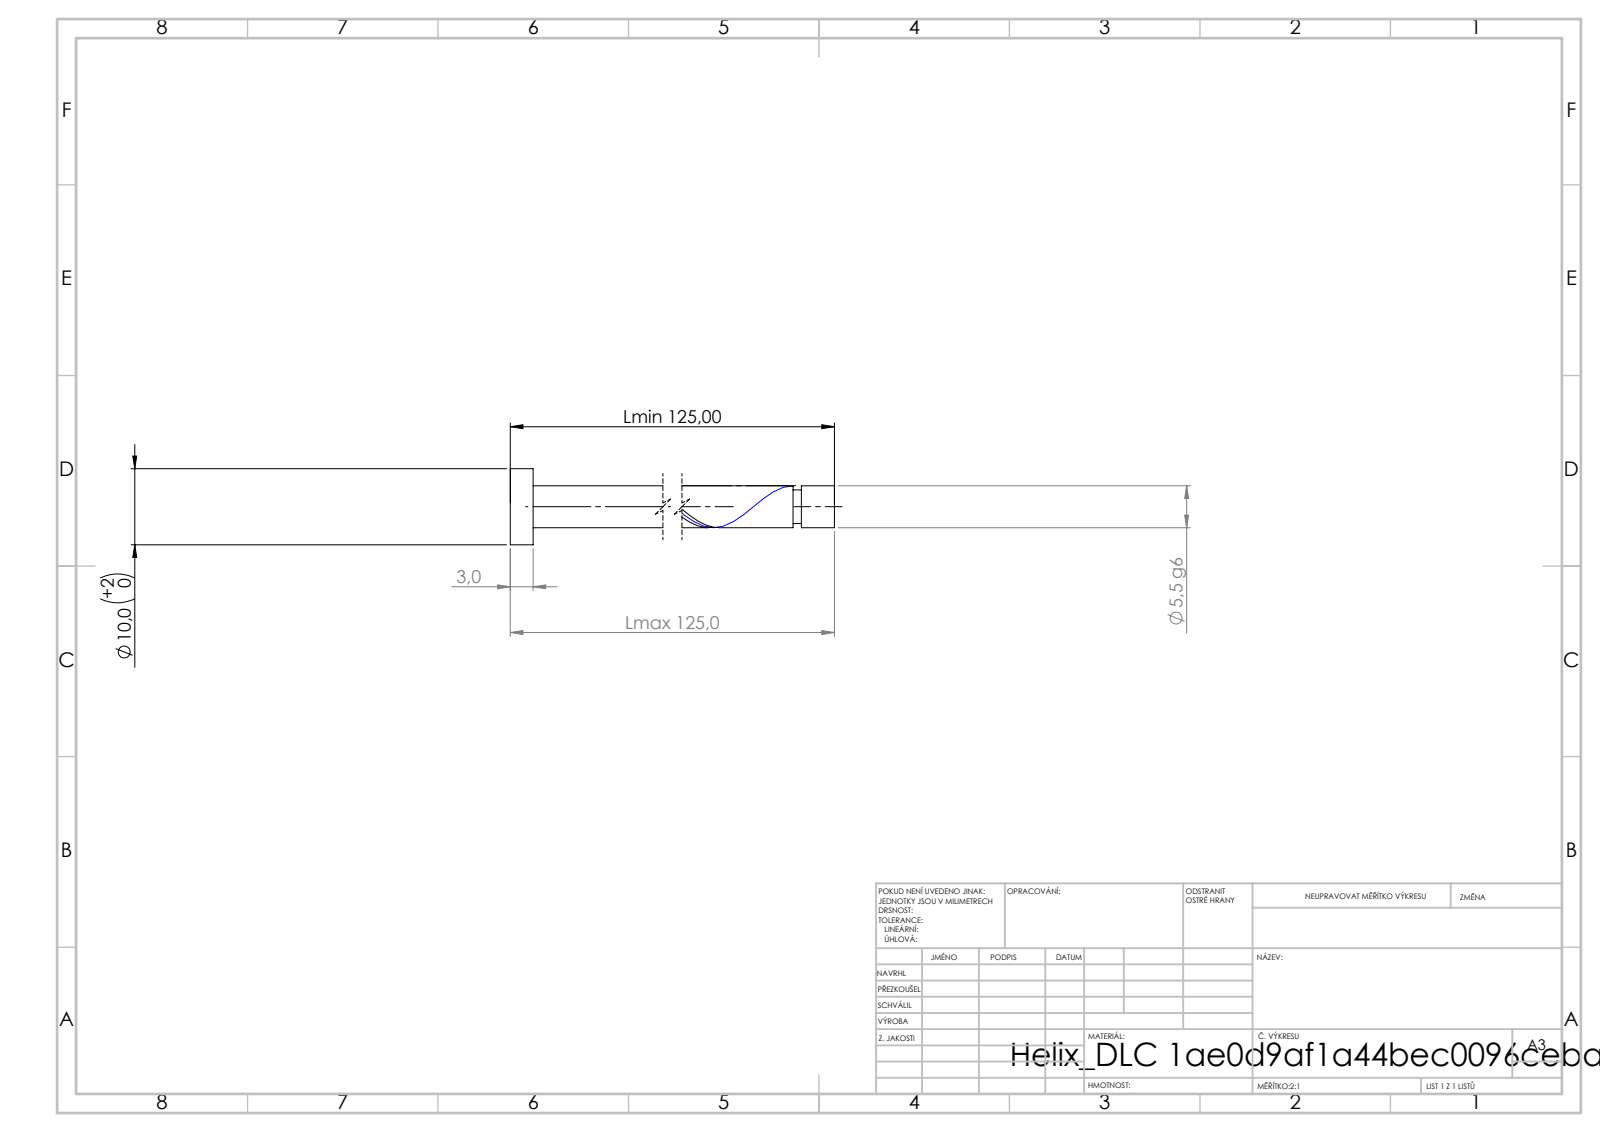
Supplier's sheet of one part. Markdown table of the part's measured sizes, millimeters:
| quantity | value |
| --- | --- |
| STEP written by | SolidWorks 2019 (CONFIG_CONTROL_DESIGN) |
| units | millimeters |
| bodies | 1 solid, 21 faces (6 planar, 14 cylindrical, 1 other) |
| overall size | 125 × 10 × 10 |
| volume | 3 096 mm³ |
| surface area | 2 420 mm² |
| round bosses / shafts (diameter × count) | 10 × 1, 5.5 × 1, 4.4 × 1 |
| main face-to-face distances | 3, 125, 122, 120.67, 117.67, 4.33, 119.57, 116.57, 1.1, 5.43 |
